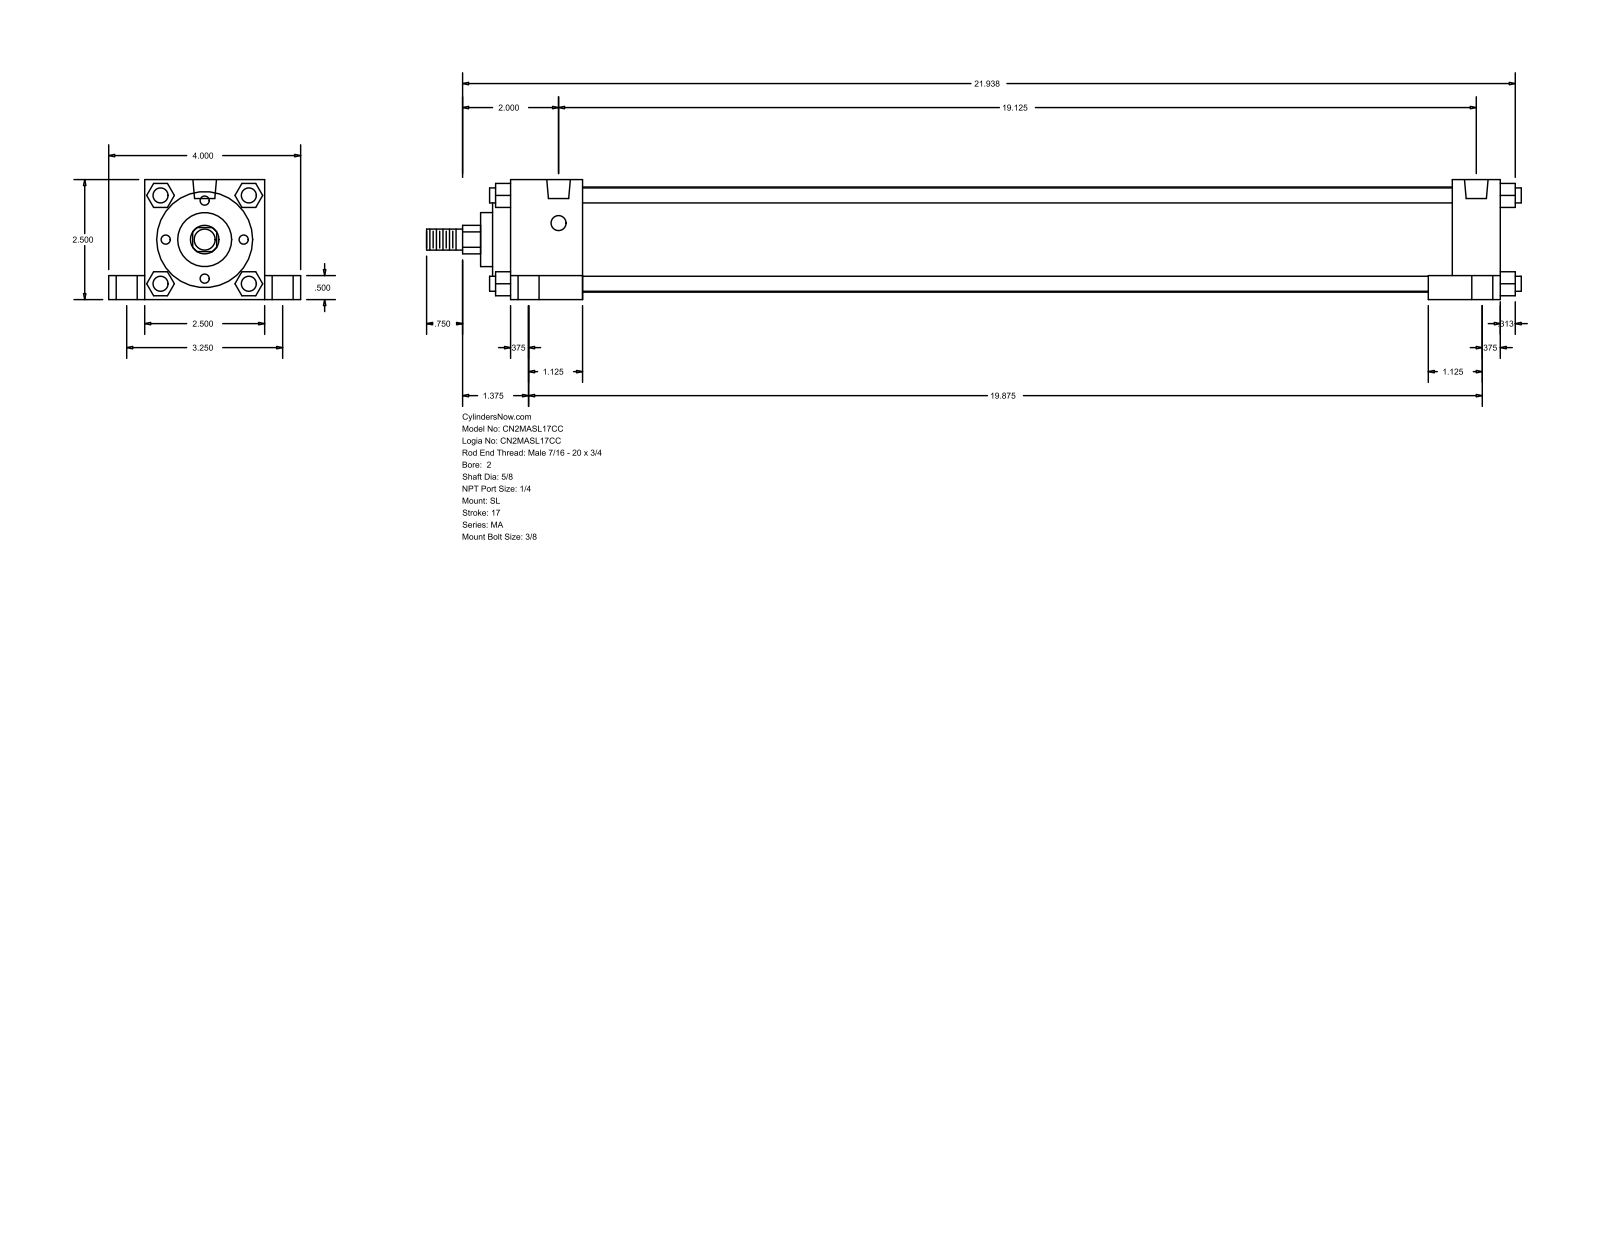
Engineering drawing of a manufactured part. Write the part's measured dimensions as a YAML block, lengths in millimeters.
part_name: "MA_SL__0200_0.625"
step_written_by: "GSSL Pune (CONFIG_CONTROL_DESIGN)"
units: millimeters
bodies: {solids: 0, faces: 150, planar: 113, cylindrical: 37, other: 0}
overall_size: [579.44, 101.6, 63.5]
round_holes:
  - {diameter: 7.94, count: 4}
  - {diameter: 11.11, count: 4}
  - {diameter: 17.46, count: 4}
  - {diameter: 12.49, count: 2}
round_bosses_or_shafts:
  - {diameter: 7.94, count: 4}
  - {diameter: 55.63, count: 1}
  - {diameter: 50.8, count: 1}
  - {diameter: 28.57, count: 1}
  - {diameter: 15.88, count: 1}
  - {diameter: 11.11, count: 1}
partial_cylinders:
  - {radius: 7.54, count: 1}
face_to_face_distances: [63.5, 12.7, 9.52, 19.05, 82.55, 38.1, 50.8, 523.87, 485.77, 498.48]
hole_center_spacings: [41.39, 44.22, 82.54, 485.78, 490.69, 503.35, 504.83, 511.53]
